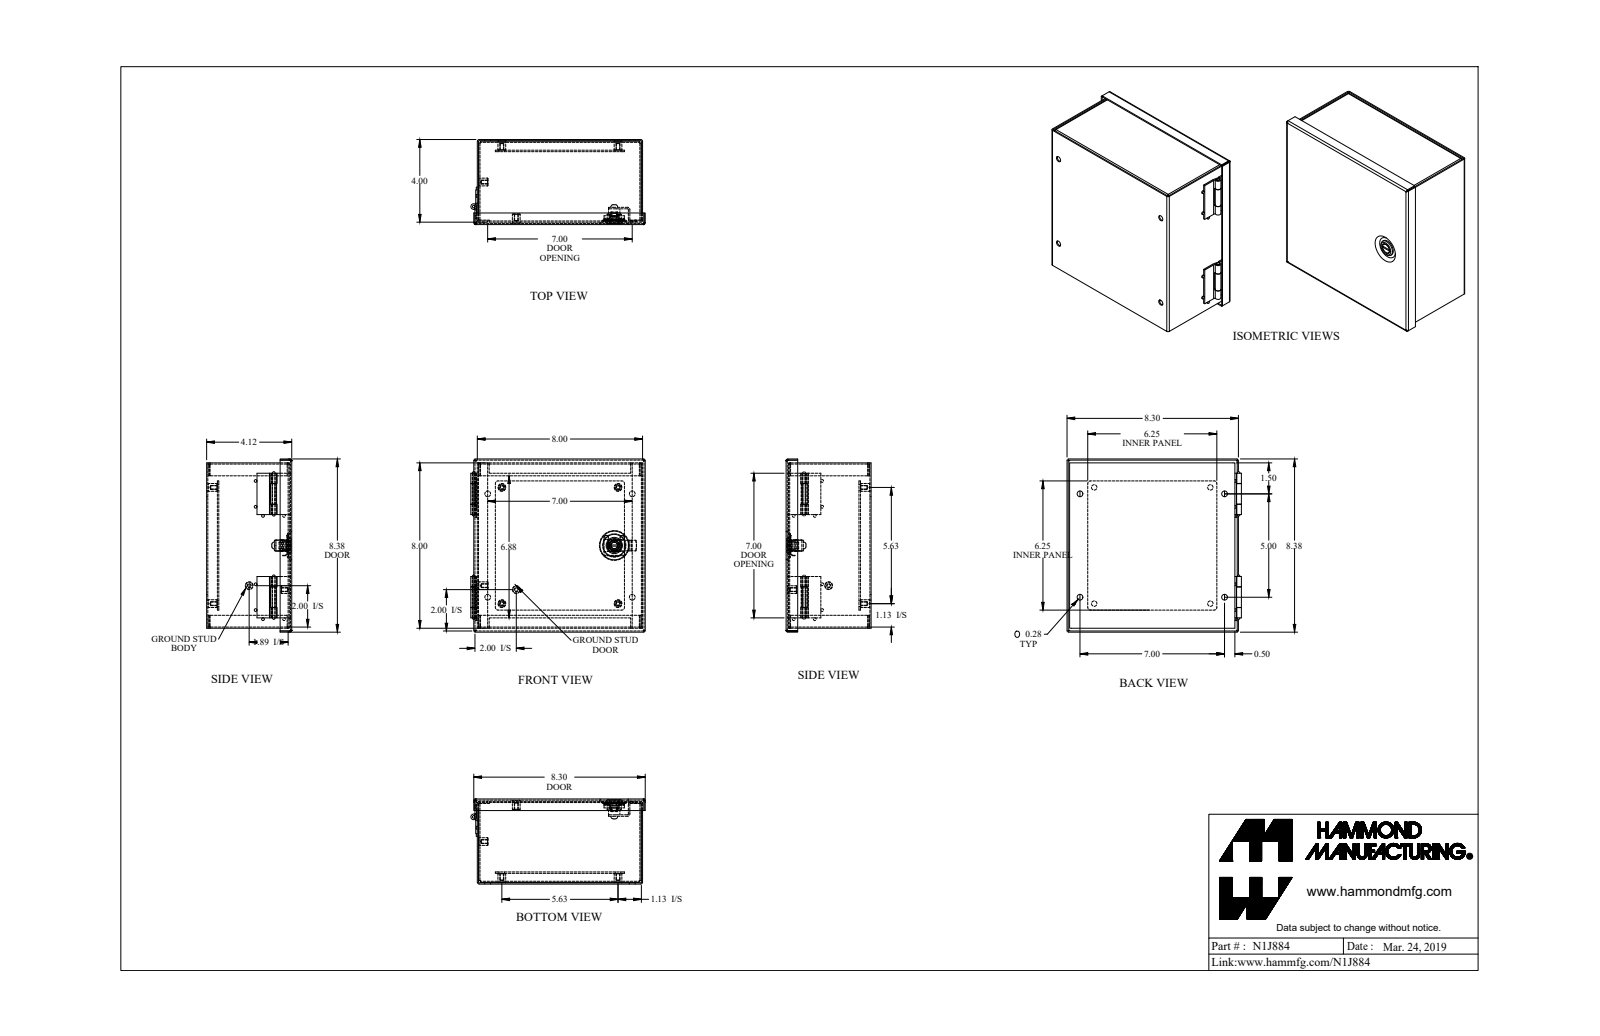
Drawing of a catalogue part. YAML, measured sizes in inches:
part_name: "N1J884"
step_written_by: "SolidWorks 2018 (AUTOMOTIVE_DESIGN)"
units: inches
bodies: {solids: 18, faces: 477, planar: 224, cylindrical: 188, other: 65}
overall_size: [8.443, 8.38, 4.118]
volume: 21.22
surface_area: 724.8
round_holes:
  - {diameter: 0.156, count: 6}
  - {diameter: 0.265, count: 4}
  - {diameter: 0.28, count: 4}
  - {diameter: 0.125, count: 1}
  - {diameter: 0.319, count: 1}
  - {diameter: 0.476, count: 1}
round_bosses_or_shafts:
  - {diameter: 0.131, count: 8}
  - {diameter: 0.375, count: 6}
  - {diameter: 0.787, count: 1}
  - {diameter: 0.547, count: 1}
  - {diameter: 0.472, count: 1}
  - {diameter: 0.469, count: 1}
  - {diameter: 0.366, count: 1}
  - {diameter: 0.32, count: 1}
partial_cylinders:
  - {radius: 0.029, count: 16}
  - {radius: 0.086, count: 16}
  - {radius: 0.012, count: 4}
  - {radius: 0.1, count: 4}
  - {radius: 0.125, count: 4}
  - {radius: 0.036, count: 2}
  - {radius: 0.079, count: 2}
  - {radius: 0.25, count: 2}
face_to_face_distances: [0.057, 4.061, 7.943, 4.004, 4.118, 8, 7.886, 0.072, 0.517, 0.46]
hole_center_spacings: [0.755, 5.357, 5.625, 6.32, 8.251, 2.648, 2.819, 5]
